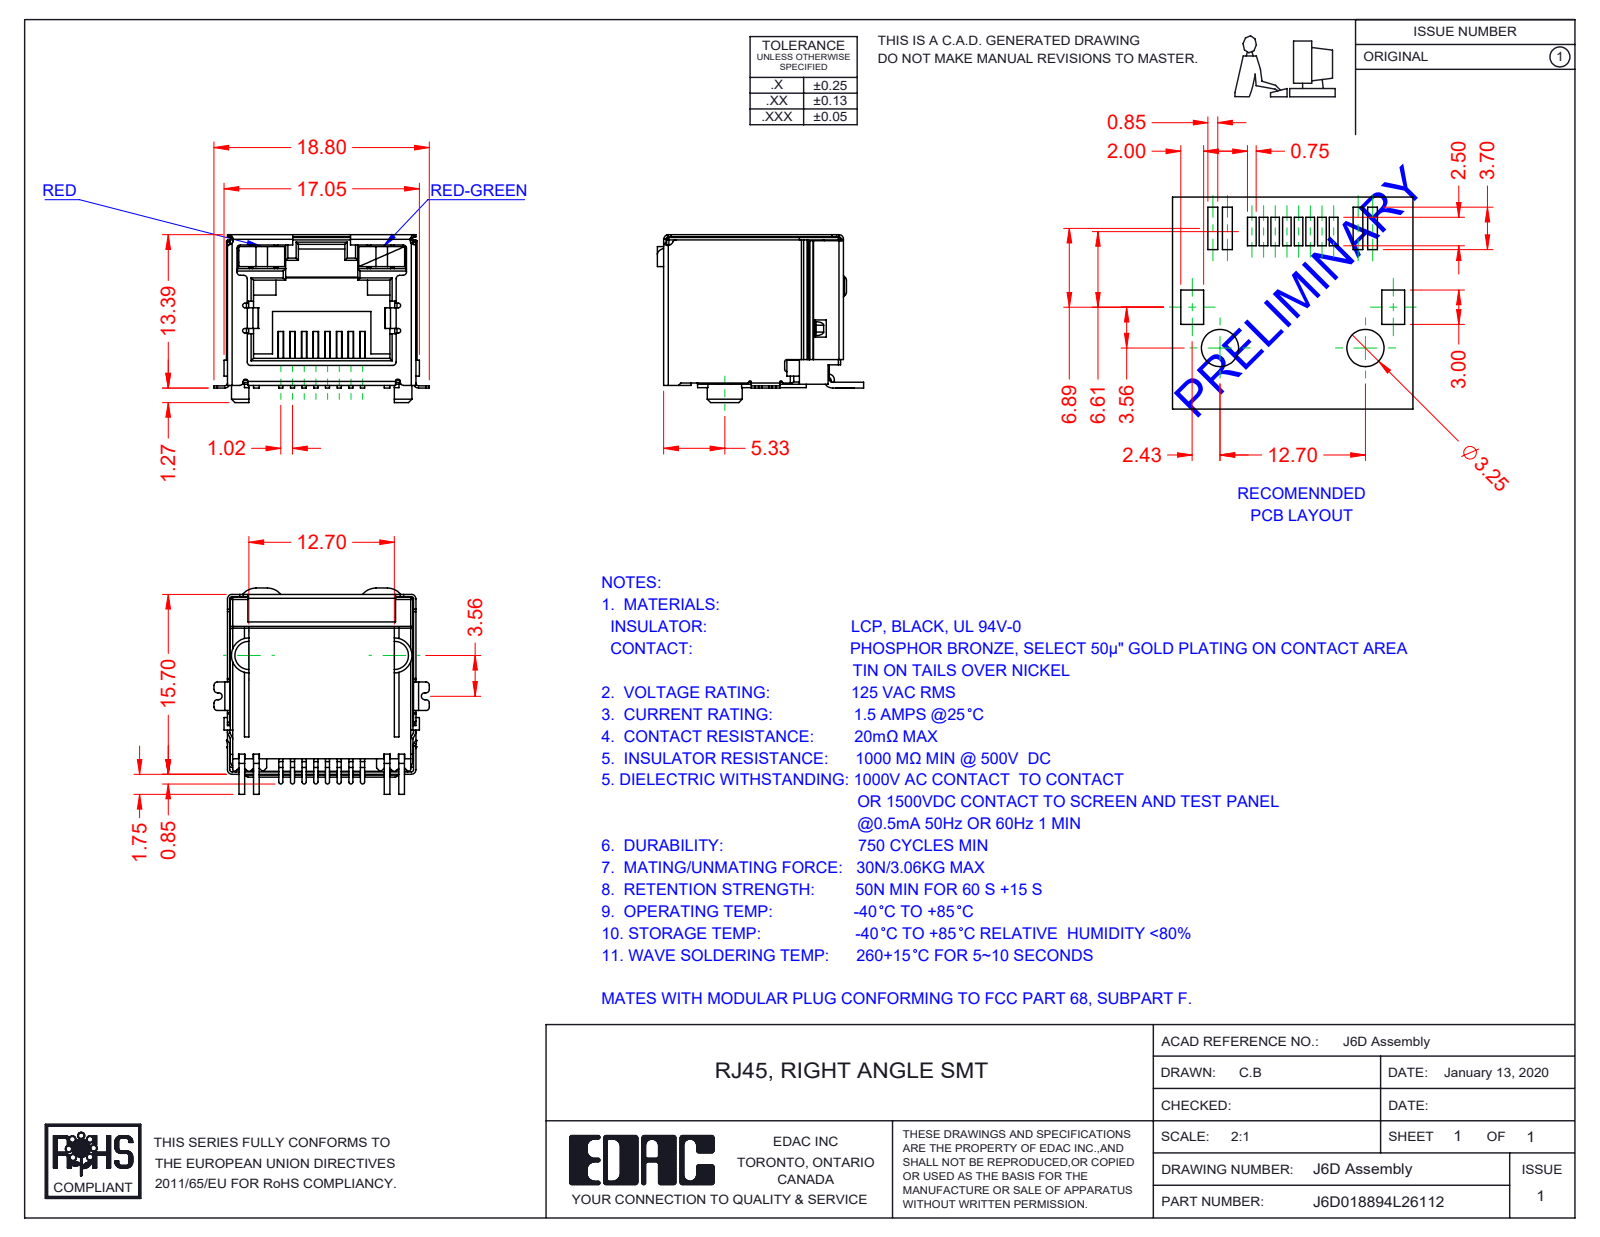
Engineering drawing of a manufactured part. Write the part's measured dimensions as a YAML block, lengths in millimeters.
part_name: "6D Shield_LED - No EMI; 6D Insulator; 6D LED LH_2-Red; J6D018894L26112 (+2 more)"
step_written_by: "SolidWorks 2016 (CONFIG_CONTROL_DESIGN)"
units: millimeters
bodies: {solids: 12, faces: 896, planar: 645, cylindrical: 218, other: 33}
overall_size: [18.8, 18, 14.65]
volume: 1804
surface_area: 4898
partial_cylinders:
  - {radius: 0.3, count: 39}
  - {radius: 0.2, count: 37}
  - {radius: 0.4, count: 16}
  - {radius: 0.1, count: 12}
  - {radius: 0.15, count: 8}
  - {radius: 0.18, count: 8}
  - {radius: 0.5, count: 6}
  - {radius: 1.5, count: 5}
face_to_face_distances: [16, 16.25, 16.2, 2.25, 1, 15.95, 16.05, 12.8, 0.45, 16.45]
